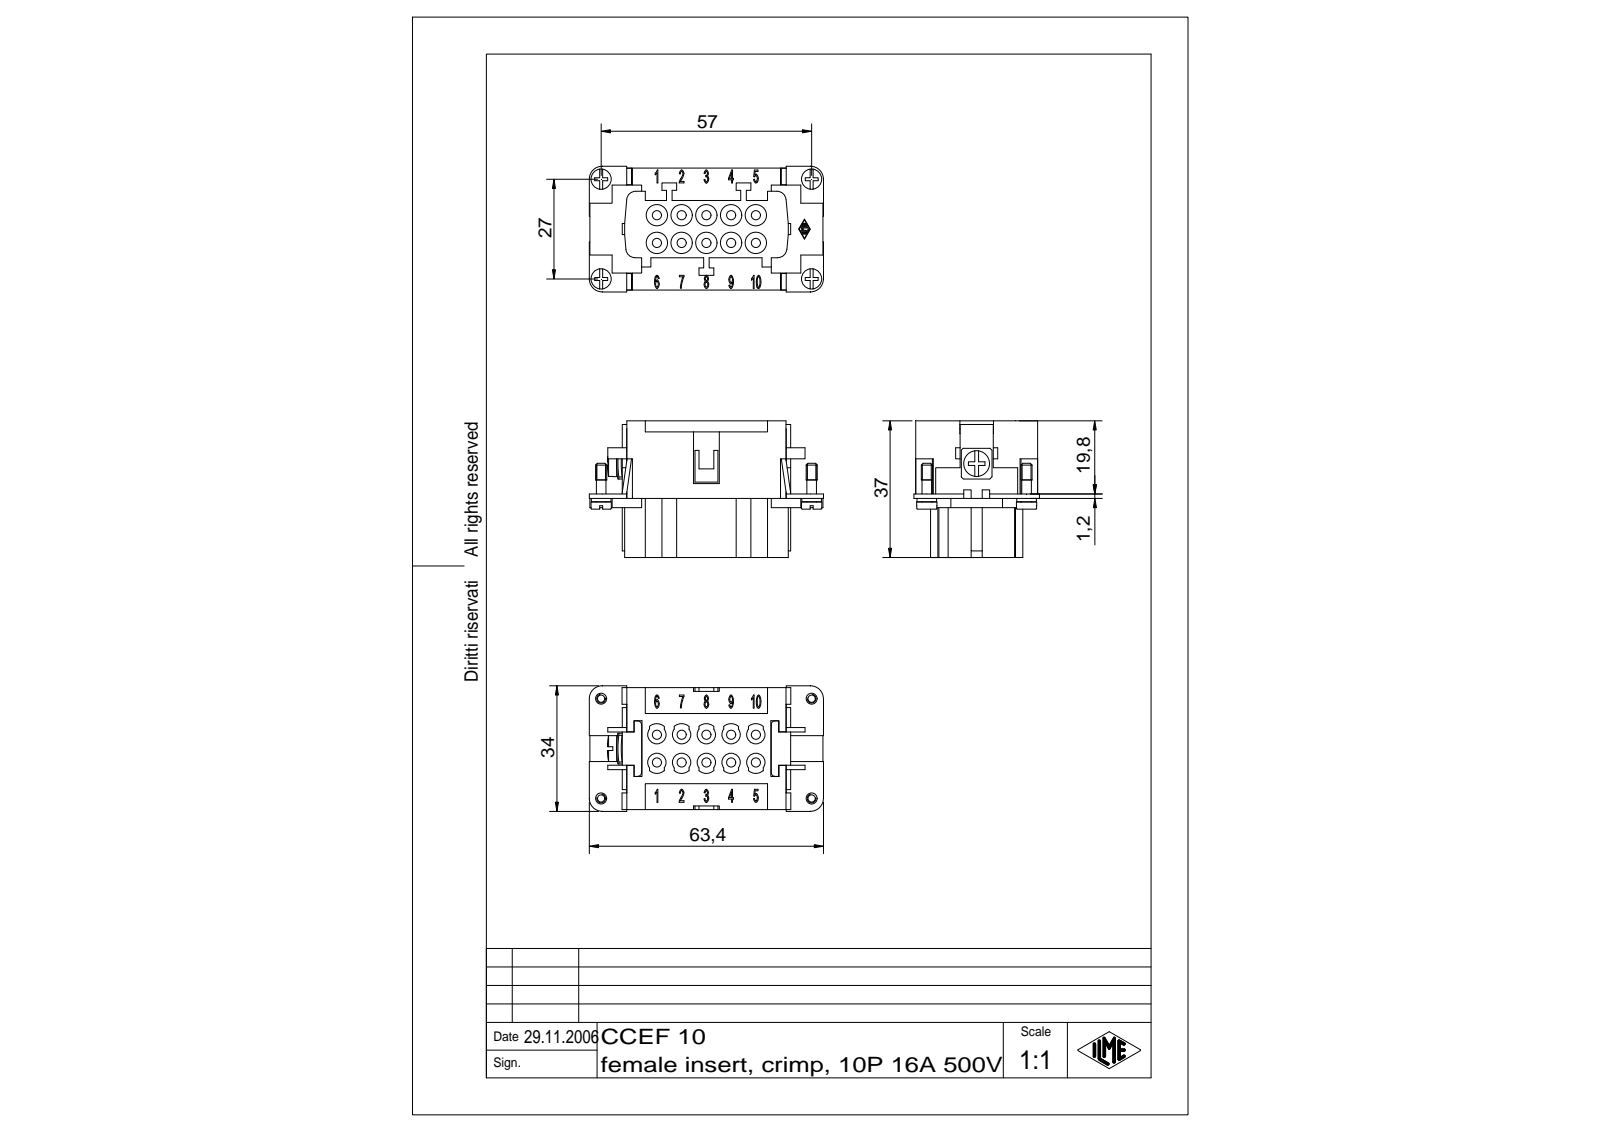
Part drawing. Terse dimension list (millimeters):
name: CCEF 10
written by: Autodesk Inventor 7 (AUTOMOTIVE_DESIGN)
unit: mm
bodies: 2 solids, 889 faces (385 planar, 65 cylindrical, 439 other)
size: 63.4 × 37 × 34
volume: 36 530 mm³; area: 19 183 mm²
holes: 1× ⌀3.24
bosses: 2× ⌀5.5, 2× ⌀5.3, 2× ⌀3, 2× ⌀2.6, 1× ⌀7
rounds: 14× R0.1, 9× R2.5, 5× R3, 2× R1, 2× R3.5, 1× R5.5
face distances: 24.25, 8.75, 21, 33, 3, 1.2, 1.5, 18, 43.1, 2.5
